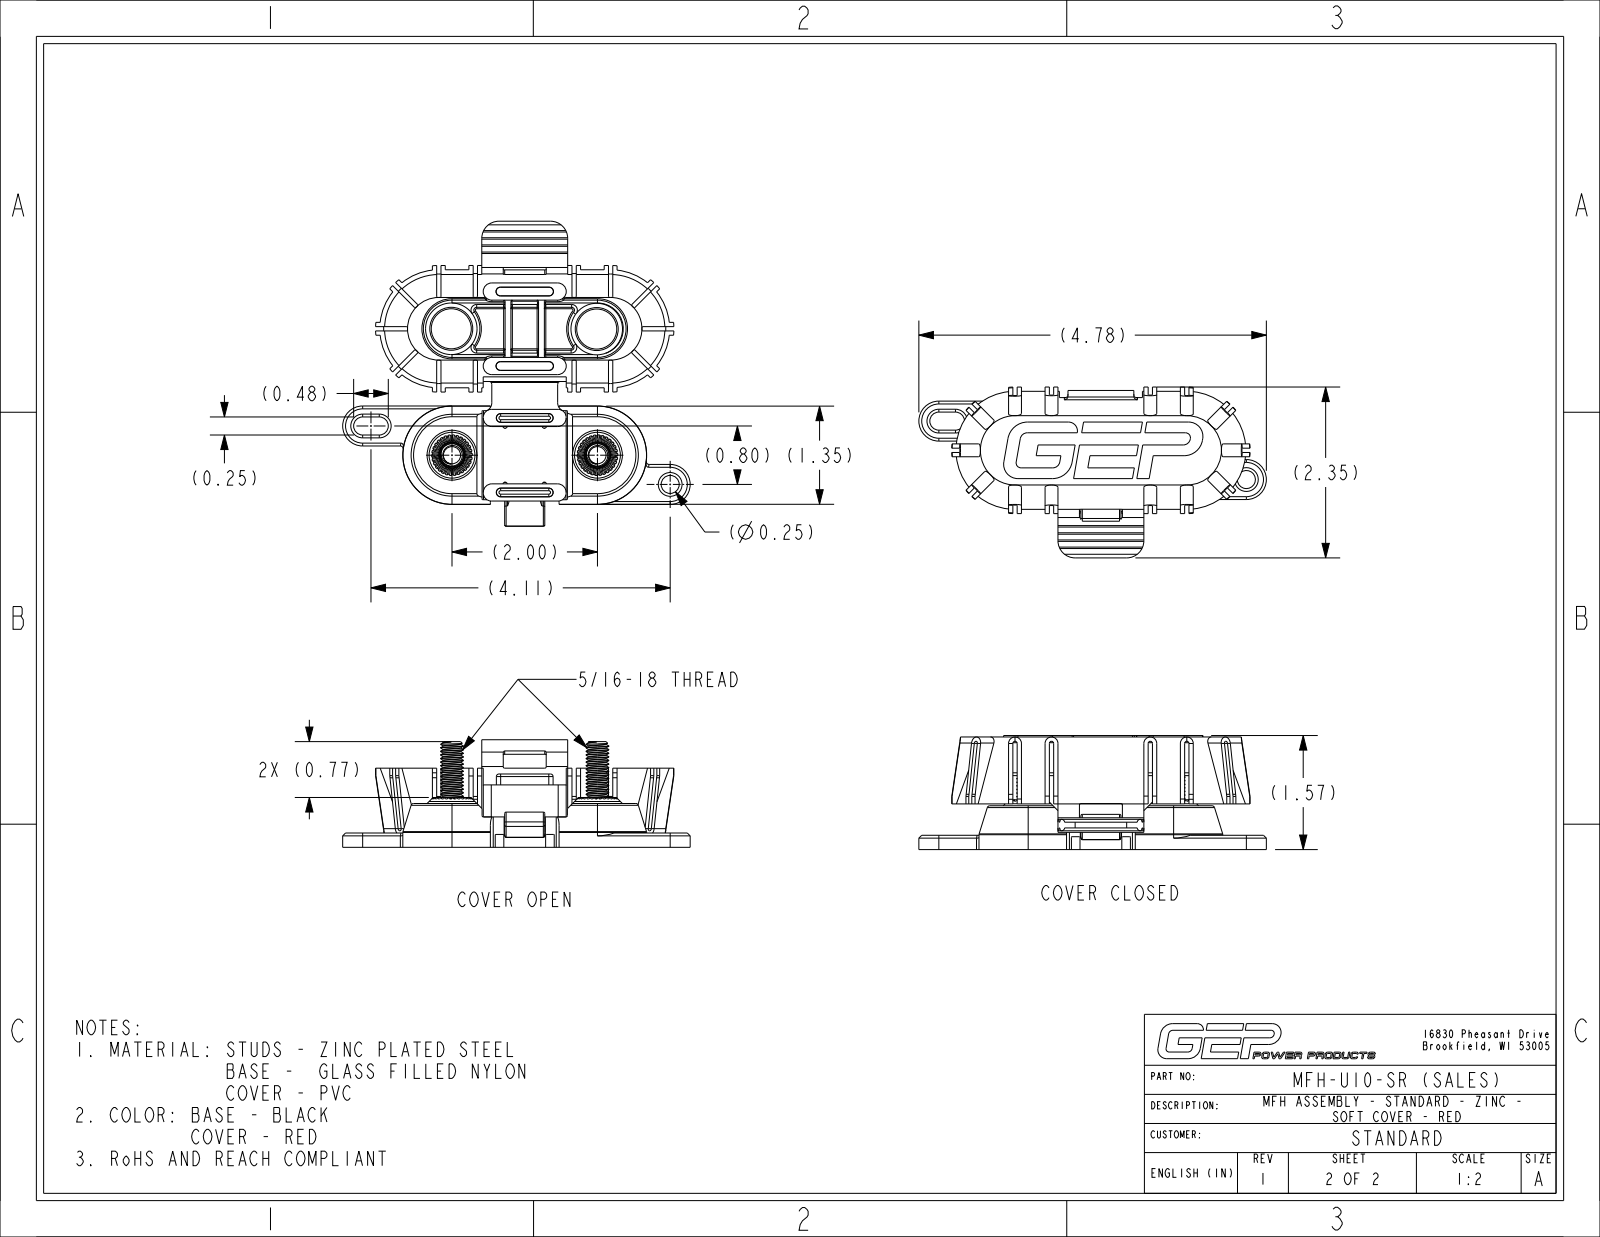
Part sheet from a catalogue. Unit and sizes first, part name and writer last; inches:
Units: inches
Overall size (bounding box): 4.778 × 2.348 × 1.568
Round holes (diameter × count): ⌀0.354 ×2, ⌀0.591 ×2, ⌀0.248 ×1
Round bosses / shafts (diameter × count): ⌀0.63 ×2, ⌀0.315 ×2
Partial cylindrical surfaces — rounded edges, fillets, slot ends (radius × count): R0.016 ×236, R0.02 ×24, R0.039 ×20, R0.02 ×14, R0.015 ×13, R0.059 ×12, R0.012 ×10, R0.035 ×10
Main face-to-face distances: 0.059, 0.118, 0.079, 0.177, 0.423, 0.02, 0.6, 1.024, 0.482, 0.541
Hole centre spacings: 2, 1.078, 1.088, 1.99, 2.01, 3.027, 3.037
Volume: 3.169 in³ · Surface area: 83.8 in²
Bodies: 4 solids, 2099 faces (769 planar, 729 cylindrical, 601 other)
Part name (STEP PRODUCT): MFH-UXX-XX_BODY_NCF; C05-1003-U1_NCF; MFH-SR_NCF_INSTALLED; MFH-U10-SR_INSTALLED_NCF_ASM
STEP written by: CREO PARAMETRIC BY PTC INC, 2024014 (CONFIG_CONTROL_DESIGN)
